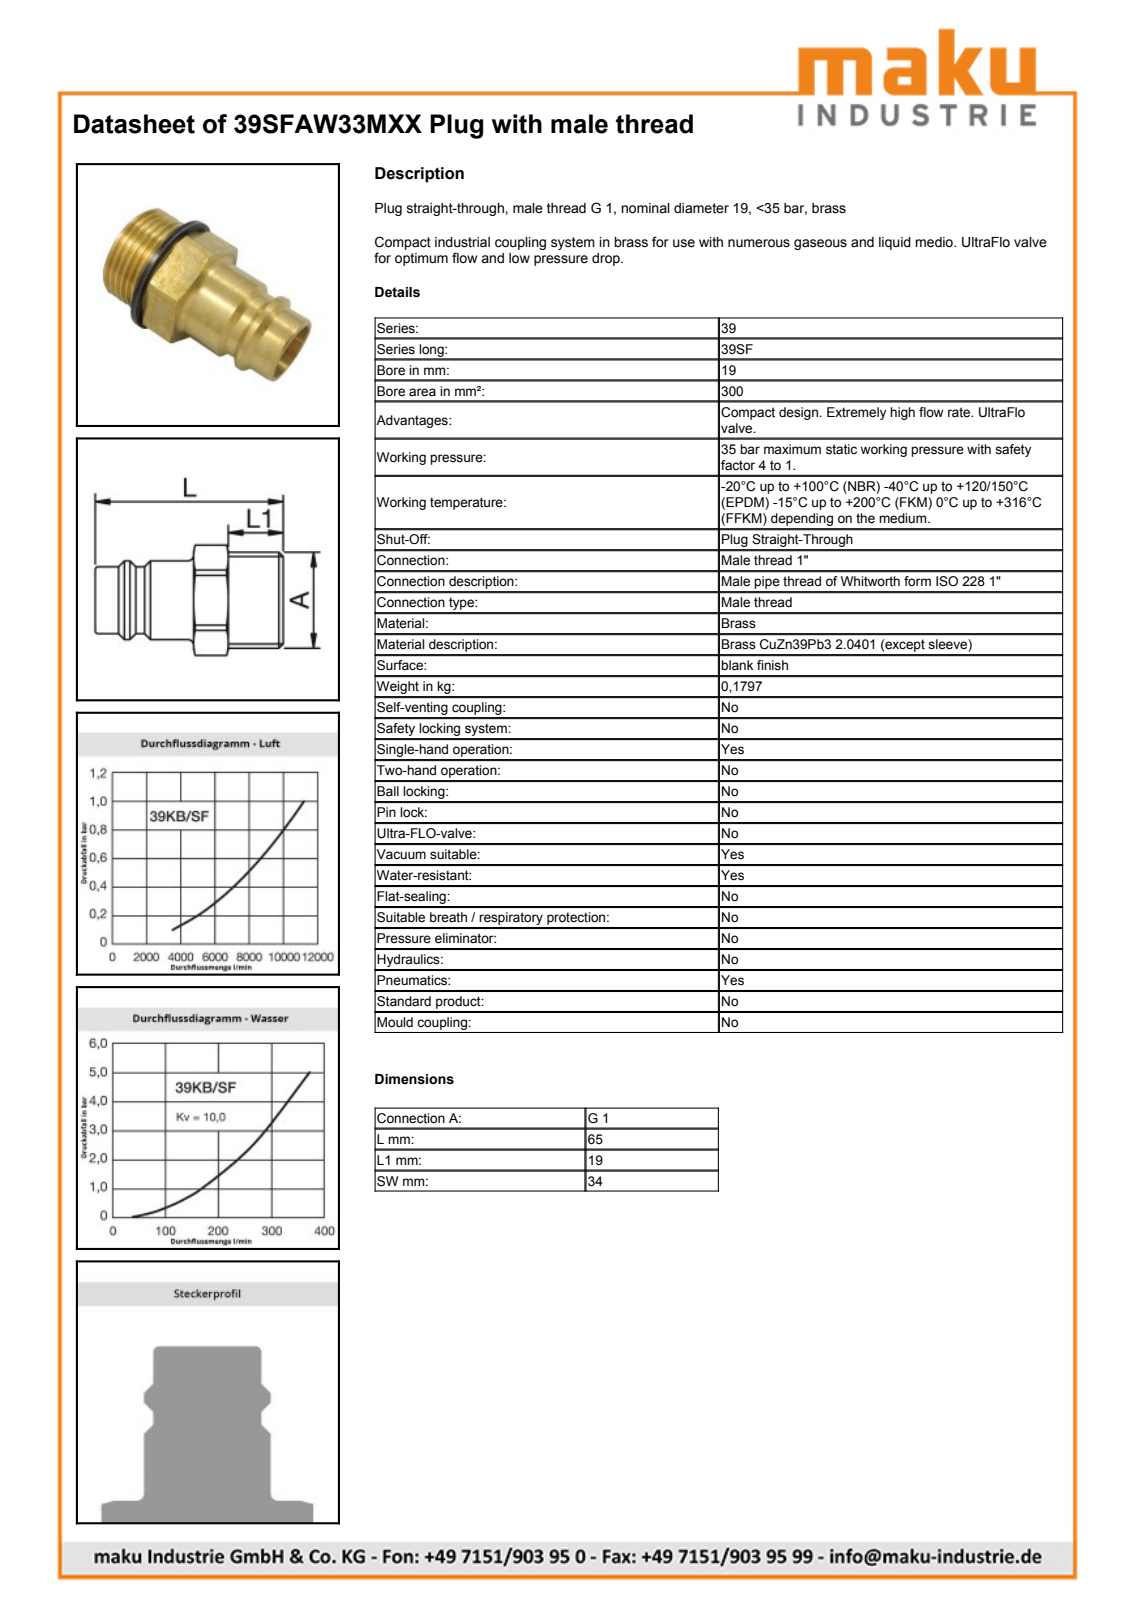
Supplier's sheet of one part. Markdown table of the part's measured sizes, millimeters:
| quantity | value |
| --- | --- |
| part name | D112485; D112479; D103698 |
| STEP written by | Autodesk Inventor 2013 (AUTOMOTIVE_DESIGN) |
| units | millimeters |
| bodies | 2 solids, 49 faces (14 planar, 16 cylindrical, 19 other) |
| overall size | 65 × 40 × 40 |
| volume | 23 398 mm³ |
| surface area | 12 835 mm² |
| round holes (diameter × count) | 19 × 1, 24 × 1, 33.4 × 1 |
| round bosses / shafts (diameter × count) | 40 × 1, 33.25 × 1, 27.2 × 1, 23.15 × 1 |
| partial cylindrical surfaces (radius × count) | 19.05 × 1 |
| main face-to-face distances | 34, 2, 19, 17, 12, 14, 31, 46, 48, 65 |
